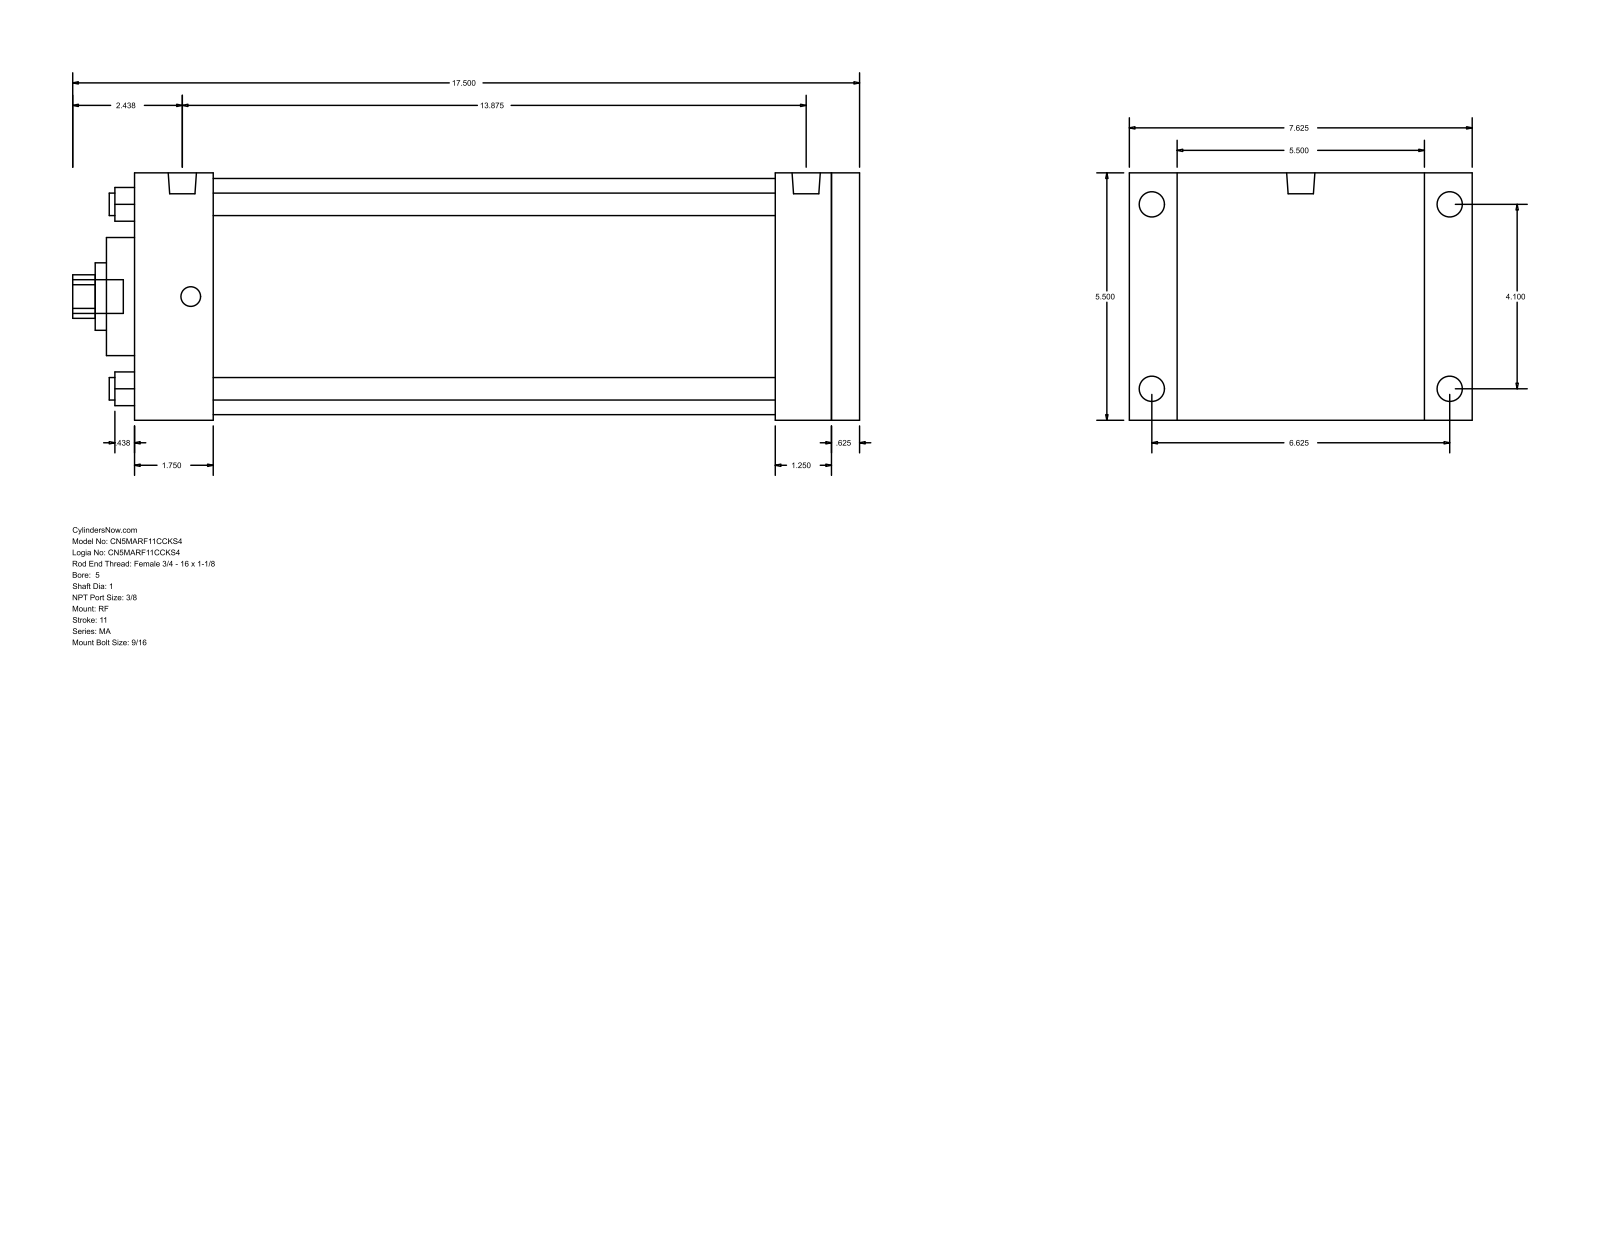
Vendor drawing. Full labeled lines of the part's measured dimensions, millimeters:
Part name (STEP PRODUCT): MA_RF__0500_1
STEP written by: GSSL Pune (CONFIG_CONTROL_DESIGN)
Units: millimetres
Bodies: 0 solids, 94 faces (65 planar, 29 cylindrical, 0 other)
Overall size (bounding box): 444.5 × 193.68 × 139.7
Round holes (diameter × count): ⌀12.7 ×4, ⌀25.4 ×1, ⌀38.1 ×1, ⌀66.67 ×1, ⌀133.35 ×1
Round bosses / shafts (diameter × count): ⌀14.29 ×4, ⌀11.11 ×4, ⌀15.93 ×2, ⌀19.05 ×1
Partial cylindrical surfaces — rounded edges, fillets, slot ends (radius × count): R12.29 ×1
Main face-to-face distances: 139.7, 409.58, 393.7, 15.88, 44.46, 349.24, 365.12, 361.96, 317.5, 31.74
Hole centre spacings: 73.64, 104.14, 147.28
